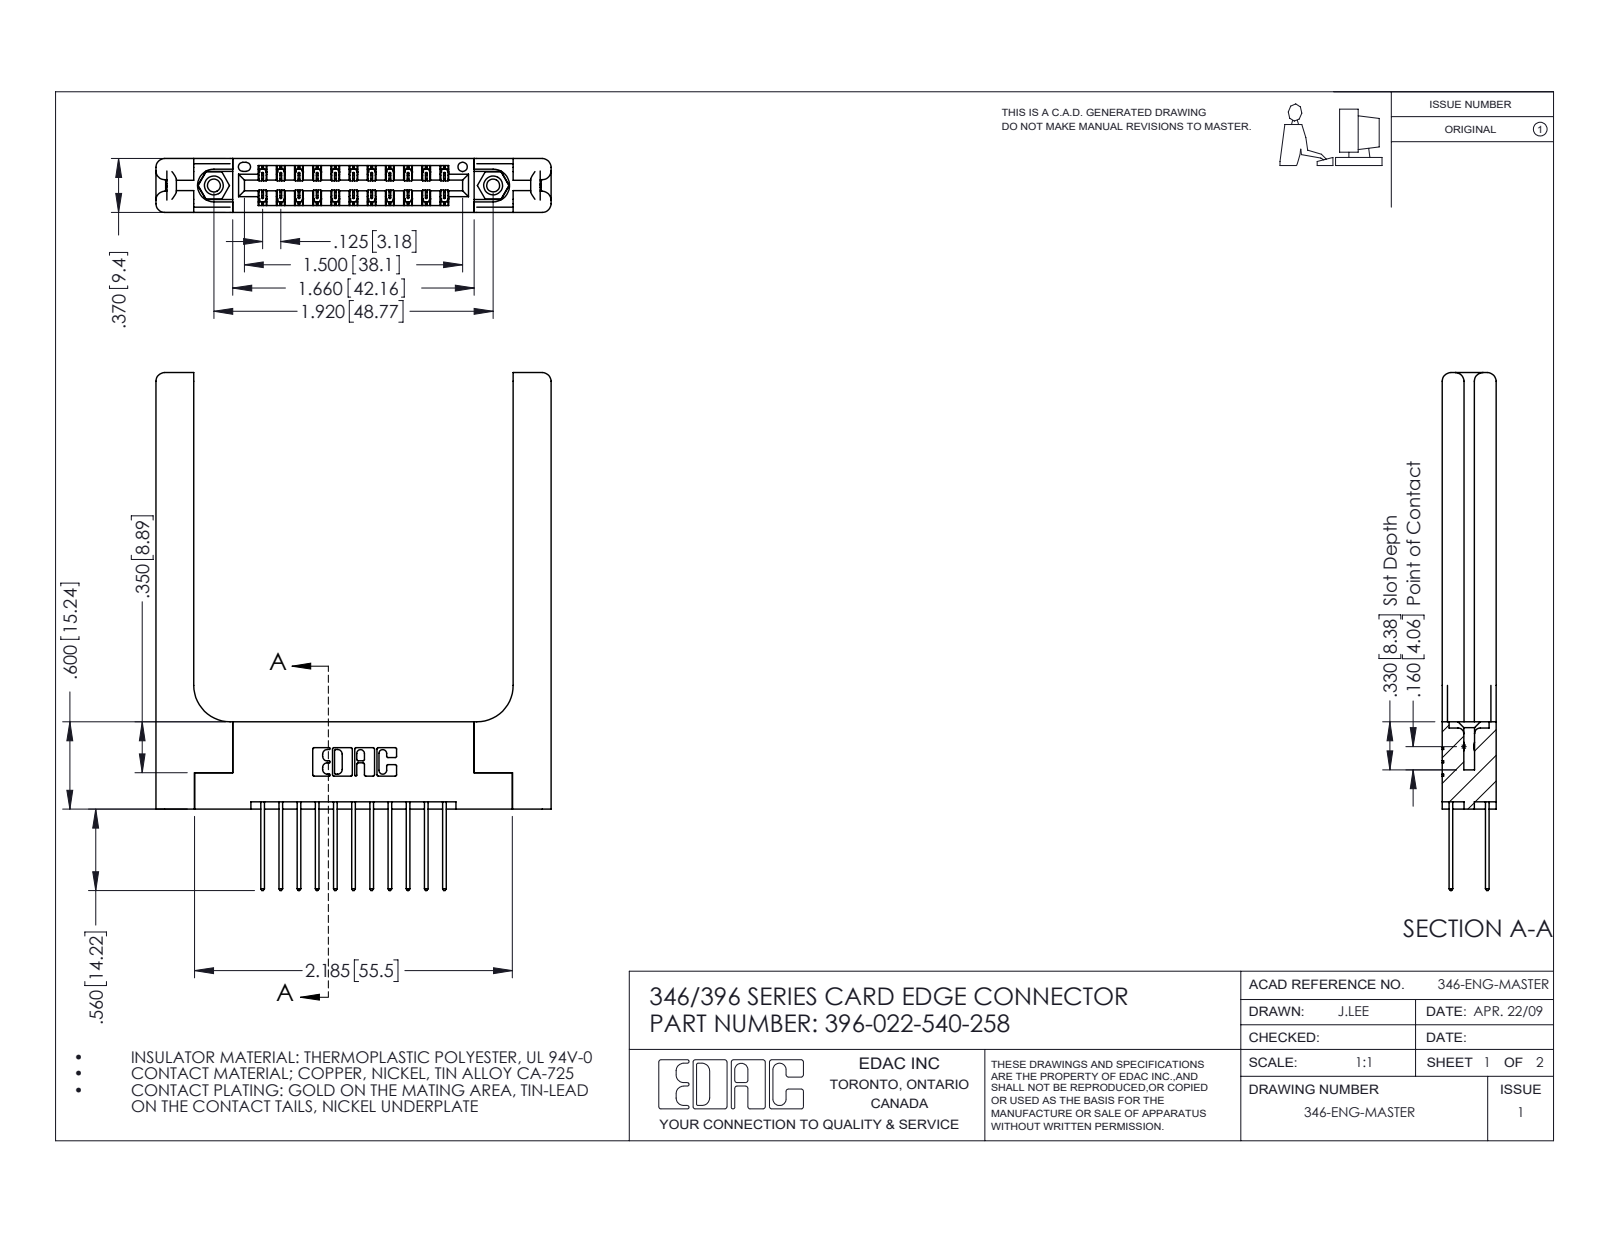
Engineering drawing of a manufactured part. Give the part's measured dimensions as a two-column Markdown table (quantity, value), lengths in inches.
| quantity | value |
| --- | --- |
| part name | 396-022-540-258; 345-250-001_345-250-001-102; 346-220-058_345-220-058; 345-292-001_345-293-140 (+1 more) |
| STEP written by | SolidWorks 2016 (CONFIG_CONTROL_DESIGN) |
| units | inches |
| bodies | 27 solids, 1522 faces (994 planar, 468 cylindrical, 60 other) |
| overall size | 3.56 × 2.716 × 0.37 |
| volume | 0.858 in³ |
| surface area | 21.56 in² |
| round holes (diameter × count) | 0.089 × 2, 0.125 × 2, 0.156 × 2, 0.064 × 1 |
| round bosses / shafts (diameter × count) | 0.155 × 2 |
| partial cylindrical surfaces (radius × count) | 0.006 × 33, 0.01 × 22, 0.01 × 22, 0.06 × 16, 0.007 × 6, 0.031 × 6, 0.026 × 3, 0.014 × 2 |
| main face-to-face distances | 0.37, 0.15, 0.072, 0.148, 0.048, 0.322, 0.25, 0.102, 0.22, 0.173 |
| hole center spacings | 0.246, 1.715, 1.92 |
